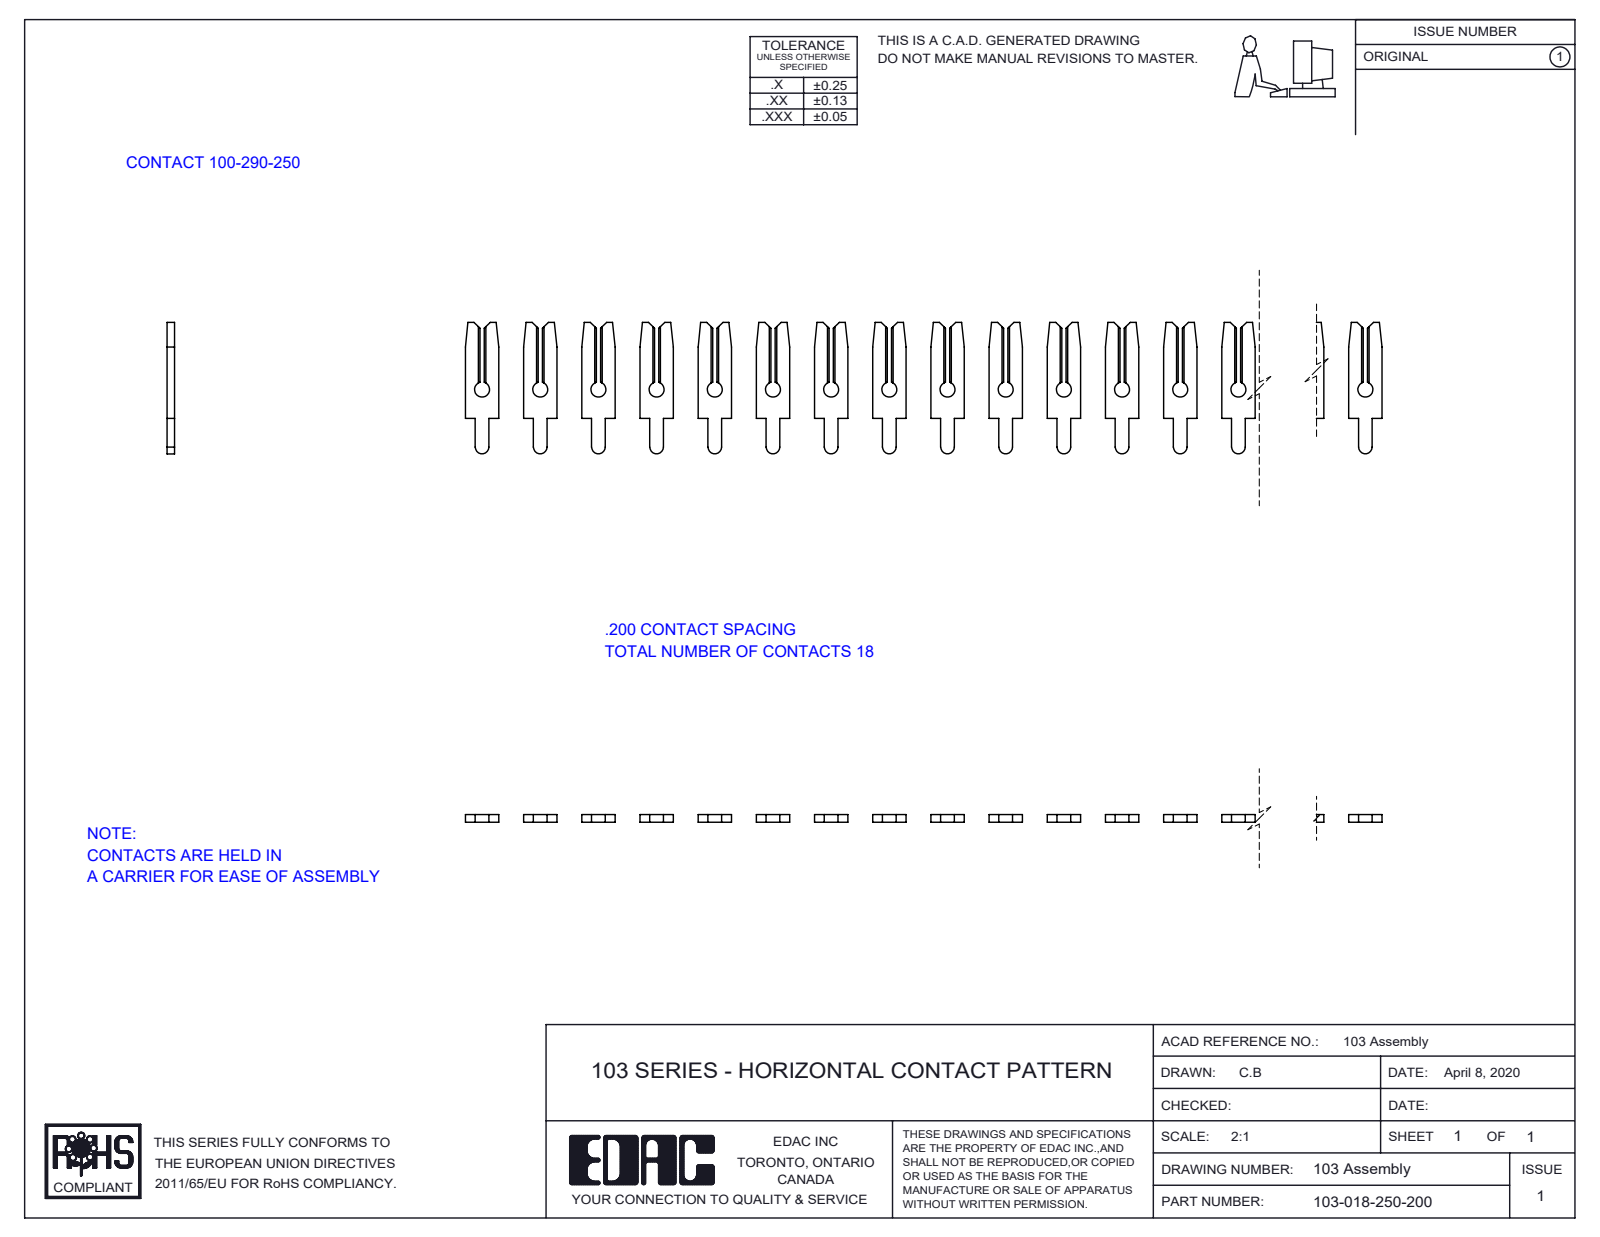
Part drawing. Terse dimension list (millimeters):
name: 103-018-250-200; 100-290-001_100-290-250
written by: SolidWorks 2016 (CONFIG_CONTROL_DESIGN)
unit: mm
bodies: 18 solids, 432 faces (360 planar, 72 cylindrical, 0 other)
size: 89.3 × 11.5 × 0.7
volume: 280 mm³; area: 1 320 mm²
holes: 18× ⌀1.3
rounds: 18× R0.6
face distances: 0.7, 5.1, 3.6, 10.2, 15.2, 21.5, 7.2, 20.3, 18, 25.1
hole spacings: 5.1, 10.2, 15.2, 20.3, 25.4, 30.5, 35.6, 40.6
